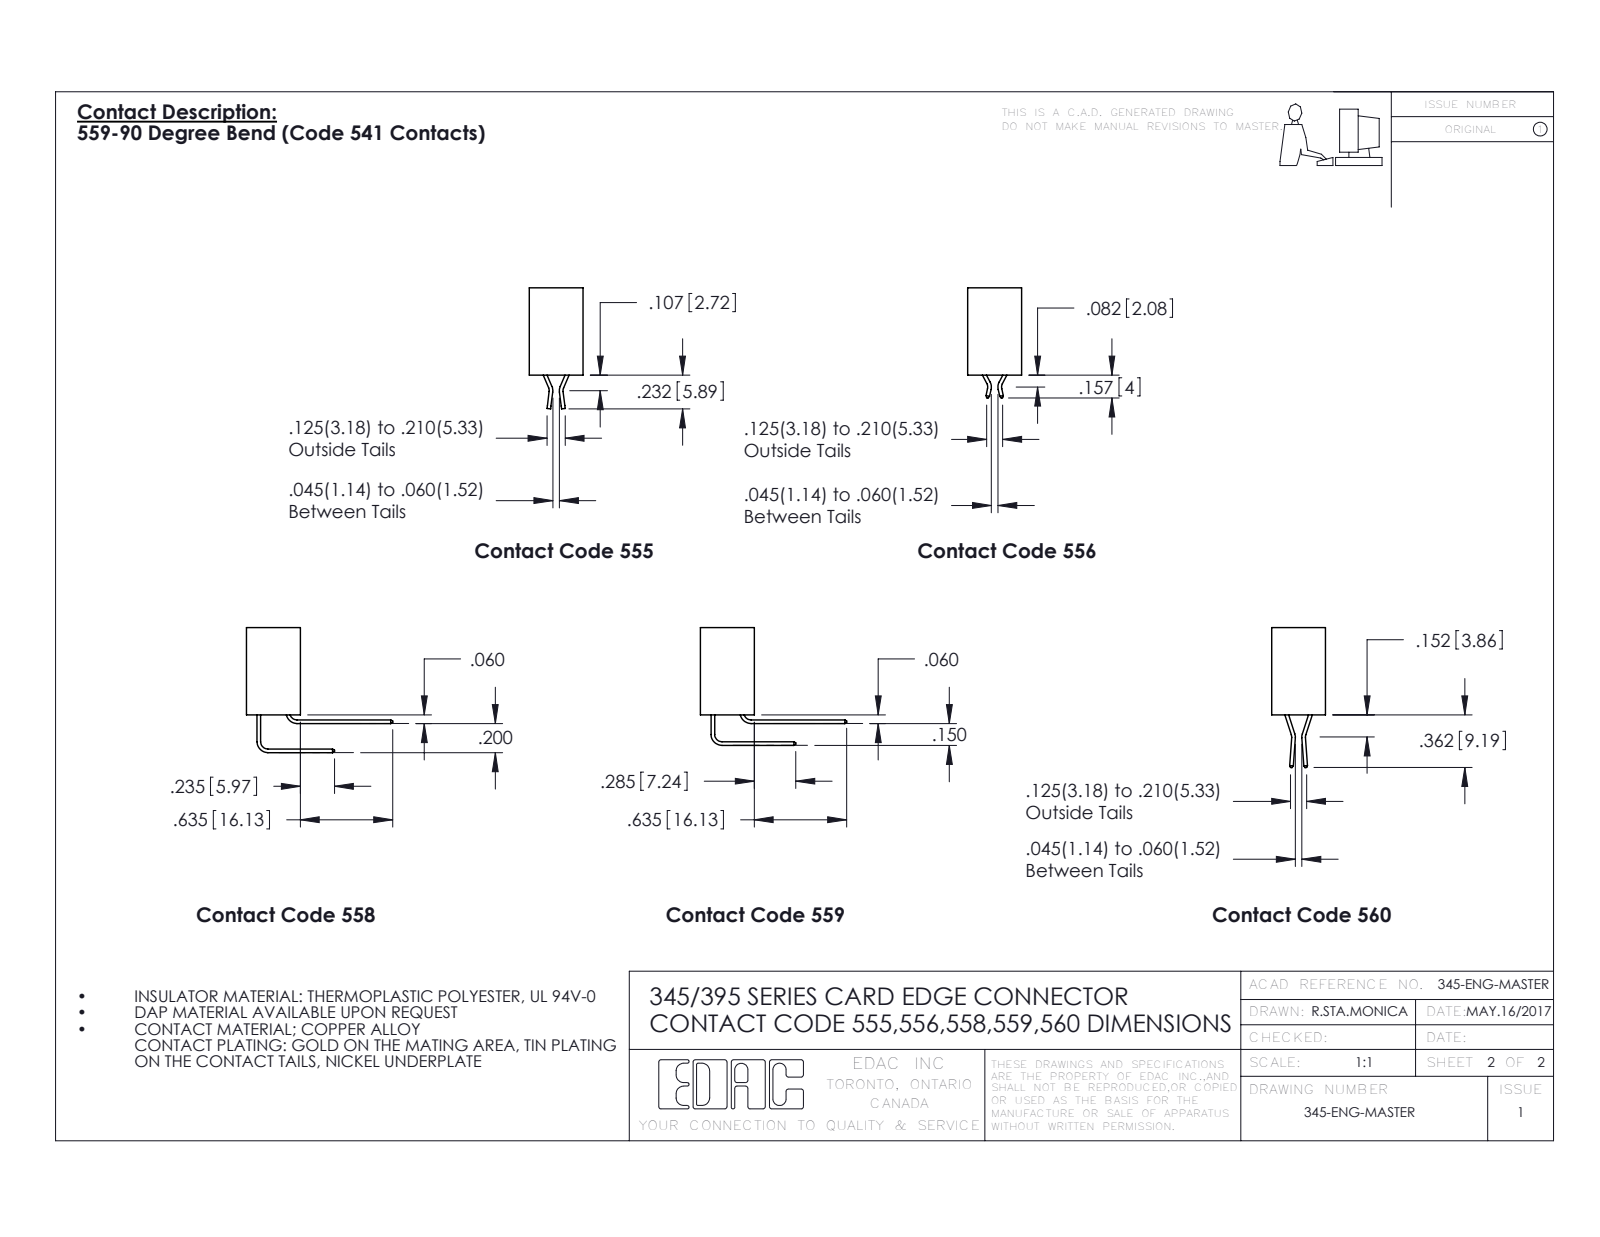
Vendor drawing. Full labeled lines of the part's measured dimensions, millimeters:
Part name (STEP PRODUCT): 345 Part_Flush Mounting Lugs - 0.156 Dia-TI; 345-292-001_558 559 Tail - 1; 395-006-559-107; 345-250-001_345-250-005-103
STEP written by: SolidWorks 2016 (CONFIG_CONTROL_DESIGN)
Units: millimetres
Bodies: 9 solids, 546 faces (364 planar, 166 cylindrical, 16 other)
Overall size (bounding box): 36.4 × 25.5 × 16.7
Volume: 3 180 mm³ · Surface area: 3 878 mm²
Round holes (diameter × count): ⌀2.5 ×2, ⌀3.2 ×2, ⌀4 ×2, ⌀1.6 ×1
Round bosses / shafts (diameter × count): ⌀3.9 ×2
Partial cylindrical surfaces — rounded edges, fillets, slot ends (radius × count): R0.3 ×22, R0.2 ×12, R0.2 ×6, R0.8 ×6, R0.7 ×3, R0.8 ×2, R1 ×2, R0.4 ×1
Main face-to-face distances: 5.1, 9.4, 2.5, 1.8, 7.6, 1.5, 7.6, 2.5, 6.9, 0.6
Hole centre spacings: 6.9, 24, 29.8
